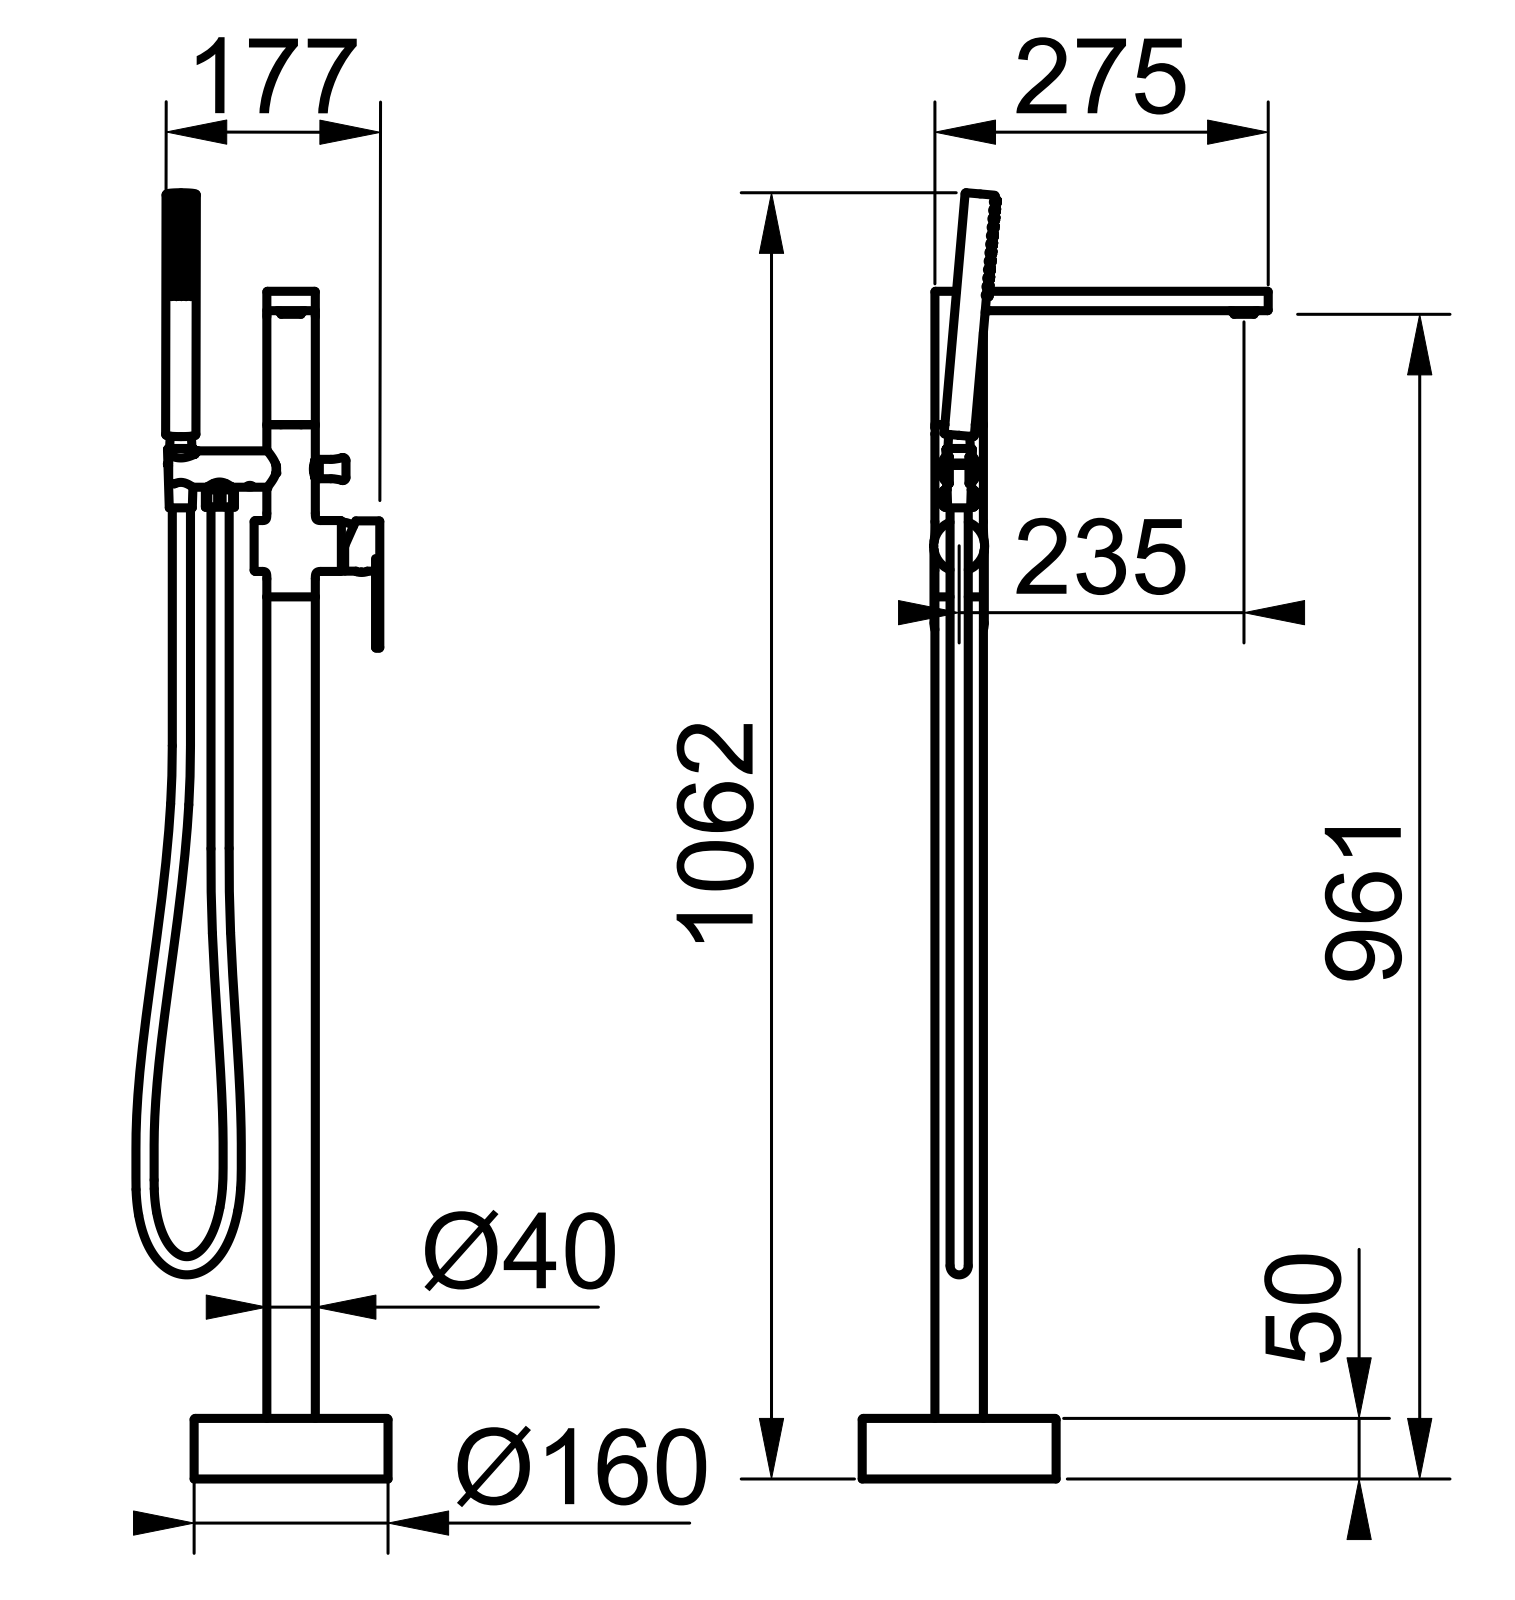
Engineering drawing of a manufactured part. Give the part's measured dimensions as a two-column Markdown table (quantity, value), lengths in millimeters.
| quantity | value |
| --- | --- |
| part name | TOM3F6418CCS8NY_1; TOM3F6418CCS8NY_7; TOM3F6418CCS8NY_8; TOM3F6418CCS8NY_9 (+8 more) |
| STEP written by | CREO PARAMETRIC BY PTC INC, 2020281 (CONFIG_CONTROL_DESIGN) |
| units | millimeters |
| bodies | 30 solids, 4072 faces (2126 planar, 1450 cylindrical, 496 other) |
| overall size | 1061.53 × 335 × 208 |
| volume | 951 588 mm³ |
| surface area | 559 436 mm² |
| round holes (diameter × count) | 0.5 × 317, 7 × 7, 8.5 × 4, 11 × 4, 4.2 × 3, 5.5 × 3, 1 × 2, 6 × 2, 13 × 2, 15 × 2, 20 × 2, 21 × 2 |
| round bosses / shafts (diameter × count) | 2.5 × 60, 22.8 × 2, 4.9 × 2, 160 × 1, 63.5 × 1, 42 × 1, 41.5 × 1, 40 × 1 |
| partial cylindrical surfaces (radius × count) | 0.5 × 18, 2 × 16, 3 × 4, 10 × 3, 3.75 × 1, 3.92 × 1, 4.15 × 1, 6.25 × 1 |
| main face-to-face distances | 2.2, 1, 13.8, 931.2, 930.2, 929, 928, 16, 915.2, 914.2 |
| hole center spacings | 7.69, 3.2, 7.7, 1.61, 6.26, 4.75, 12.45, 10.3 |
